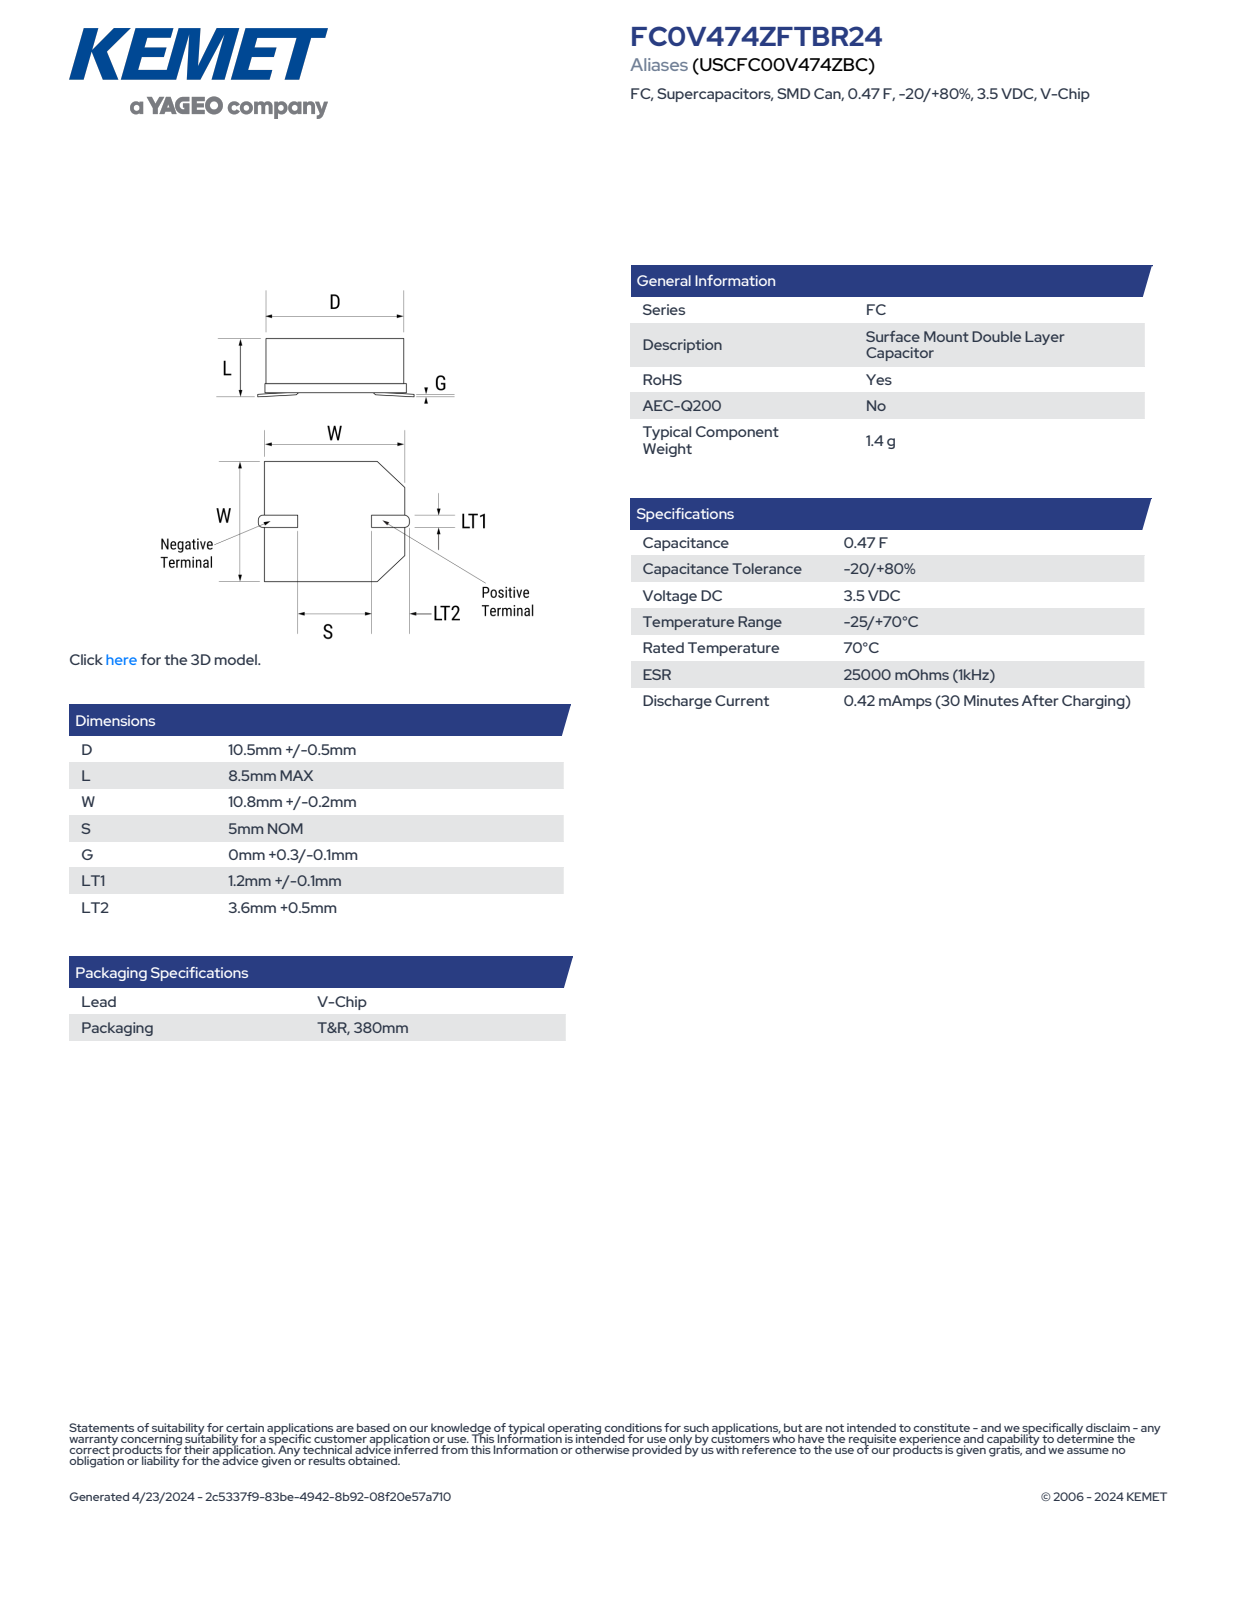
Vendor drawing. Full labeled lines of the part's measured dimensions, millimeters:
Part name (STEP PRODUCT): CDC_VC_D10.5L8.5LT11.3G0.3W11LT24.1
STEP written by: SolidWorks 2014 (AUTOMOTIVE_DESIGN)
Units: millimetres
Bodies: 5 solids, 60 faces (49 planar, 5 cylindrical, 6 other)
Overall size (bounding box): 13.2 × 11 × 8.51
Volume: 766 mm³ · Surface area: 716 mm²
Round bosses / shafts (diameter × count): ⌀10.5 ×1
Partial cylindrical surfaces — rounded edges, fillets, slot ends (radius × count): R0.2 ×2, R4.17 ×1
Main face-to-face distances: 2.12, 8.2, 6.08, 11, 2.42, 8.5, 4.85, 6.15, 1.3, 1.1
